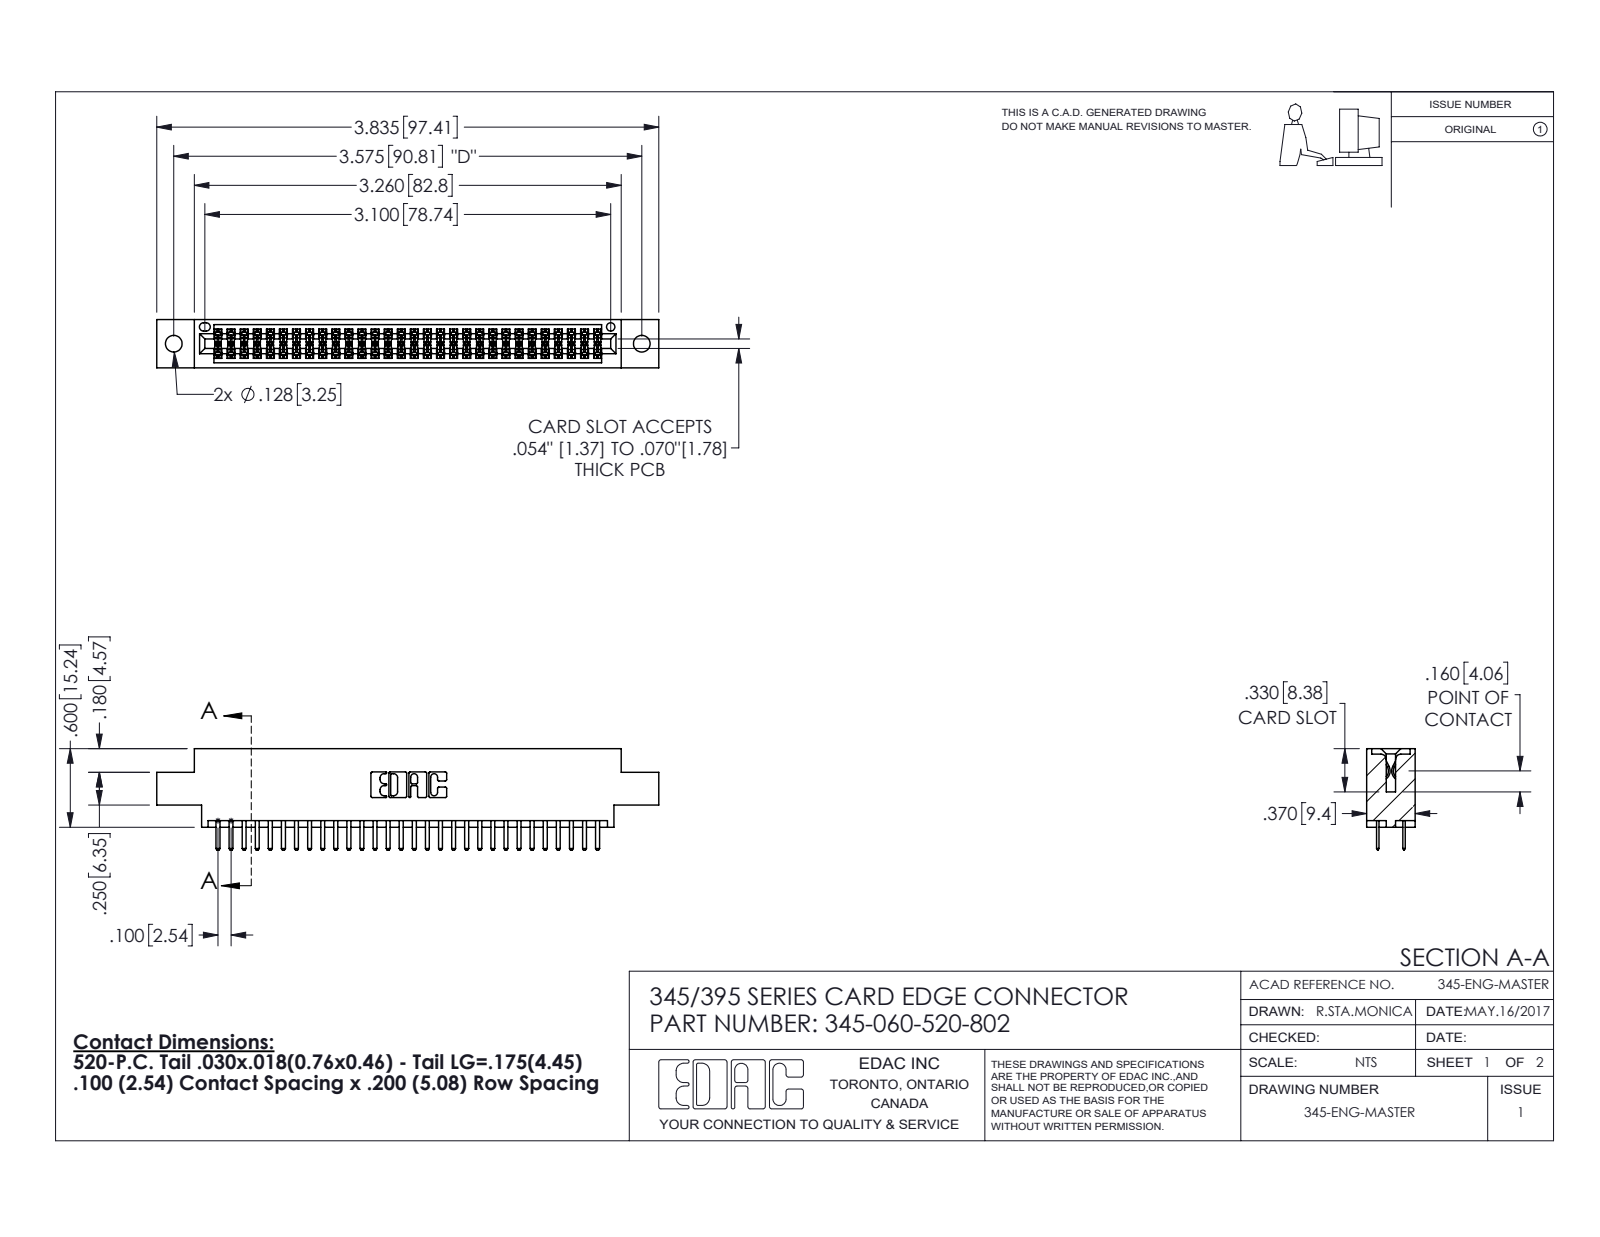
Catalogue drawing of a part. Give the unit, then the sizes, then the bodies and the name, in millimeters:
Units: millimetres
Overall size (bounding box): 97.4 × 19.7 × 9.4
Round holes (diameter × count): ⌀3.3 ×2, ⌀1.6 ×1
Partial cylindrical surfaces — rounded edges, fillets, slot ends (radius × count): R0.2 ×90, R0.3 ×64, R0.3 ×22, R0.2 ×6, R0.8 ×6, R0.7 ×3, R0.4 ×2, R0.5 ×2
Main face-to-face distances: 1.8, 7.6, 5.1, 9.4, 2.5, 6.9, 0.6, 5.7, 0.6, 4.4
Hole centre spacings: 6.9, 84.8, 90.8
Volume: 9 180 mm³ · Surface area: 13 140 mm²
Bodies: 61 solids, 3370 faces (2184 planar, 1186 cylindrical, 0 other)
Part name (STEP PRODUCT): 345-292-001_345-293-120; 345 Part_0.170 Offset - 0.128 Dia; 345-060-520-802
STEP written by: SolidWorks 2016 (CONFIG_CONTROL_DESIGN)
